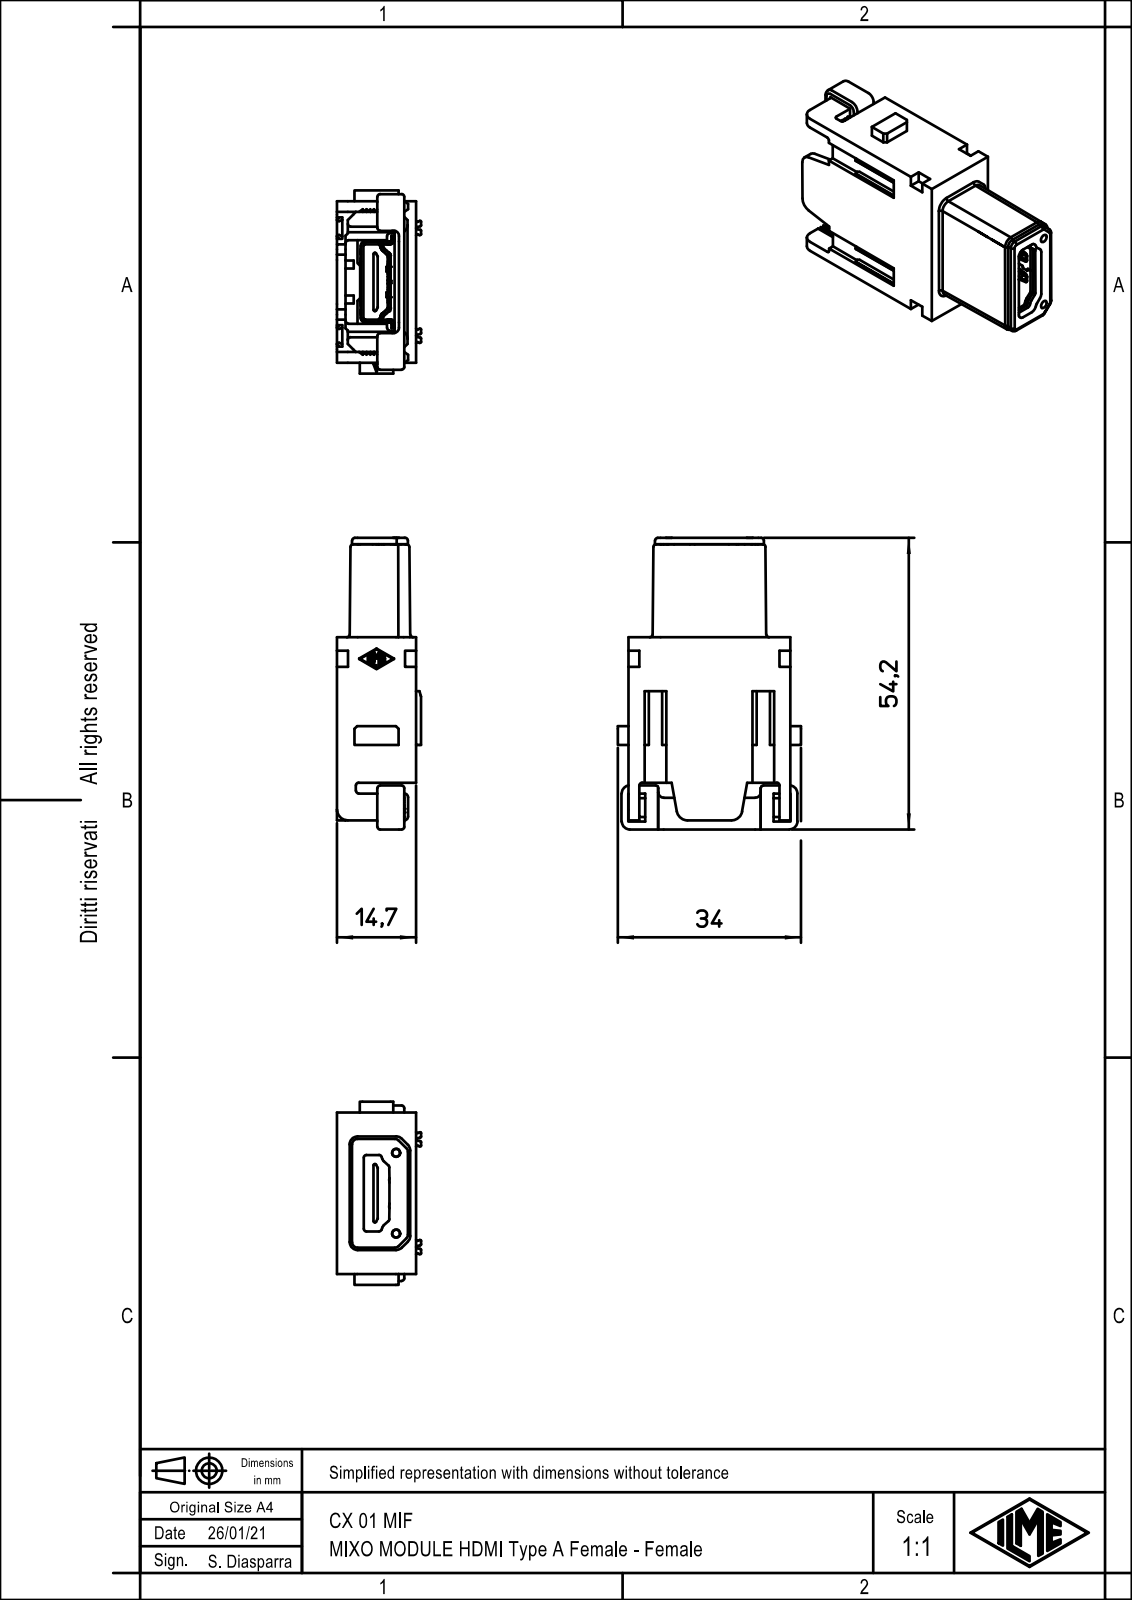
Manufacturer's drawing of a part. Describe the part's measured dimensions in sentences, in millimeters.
The part is named "CX_01_MIF". Its 3-D file was written by "Creo Elements/Direct Modeling 20.1B 02-Apr-2019 (C) Parametric Technology GmbH (AUTOMOTIVE_DESIGN)". It is 1 solid with 289 faces: 190 planar, 73 cylindrical and 26 other. Overall it measures 54.15 by 34 by 15.6 millimeters. Its volume is 14 725 cubic millimeters and its surface area 6 876 square millimeters. Partial cylindrical surfaces (rounded edges, fillets, slot ends): 35 of radius 0.5, 12 of radius 1, 10 of radius 1.5, 7 of radius 2, 2 of radius 0.4, 2 of radius 0.7. The main face-to-face distances are 14.7, 11.35, 30, 3.35, 1.75, 2.35, 1, 6.25, 8, 4.
